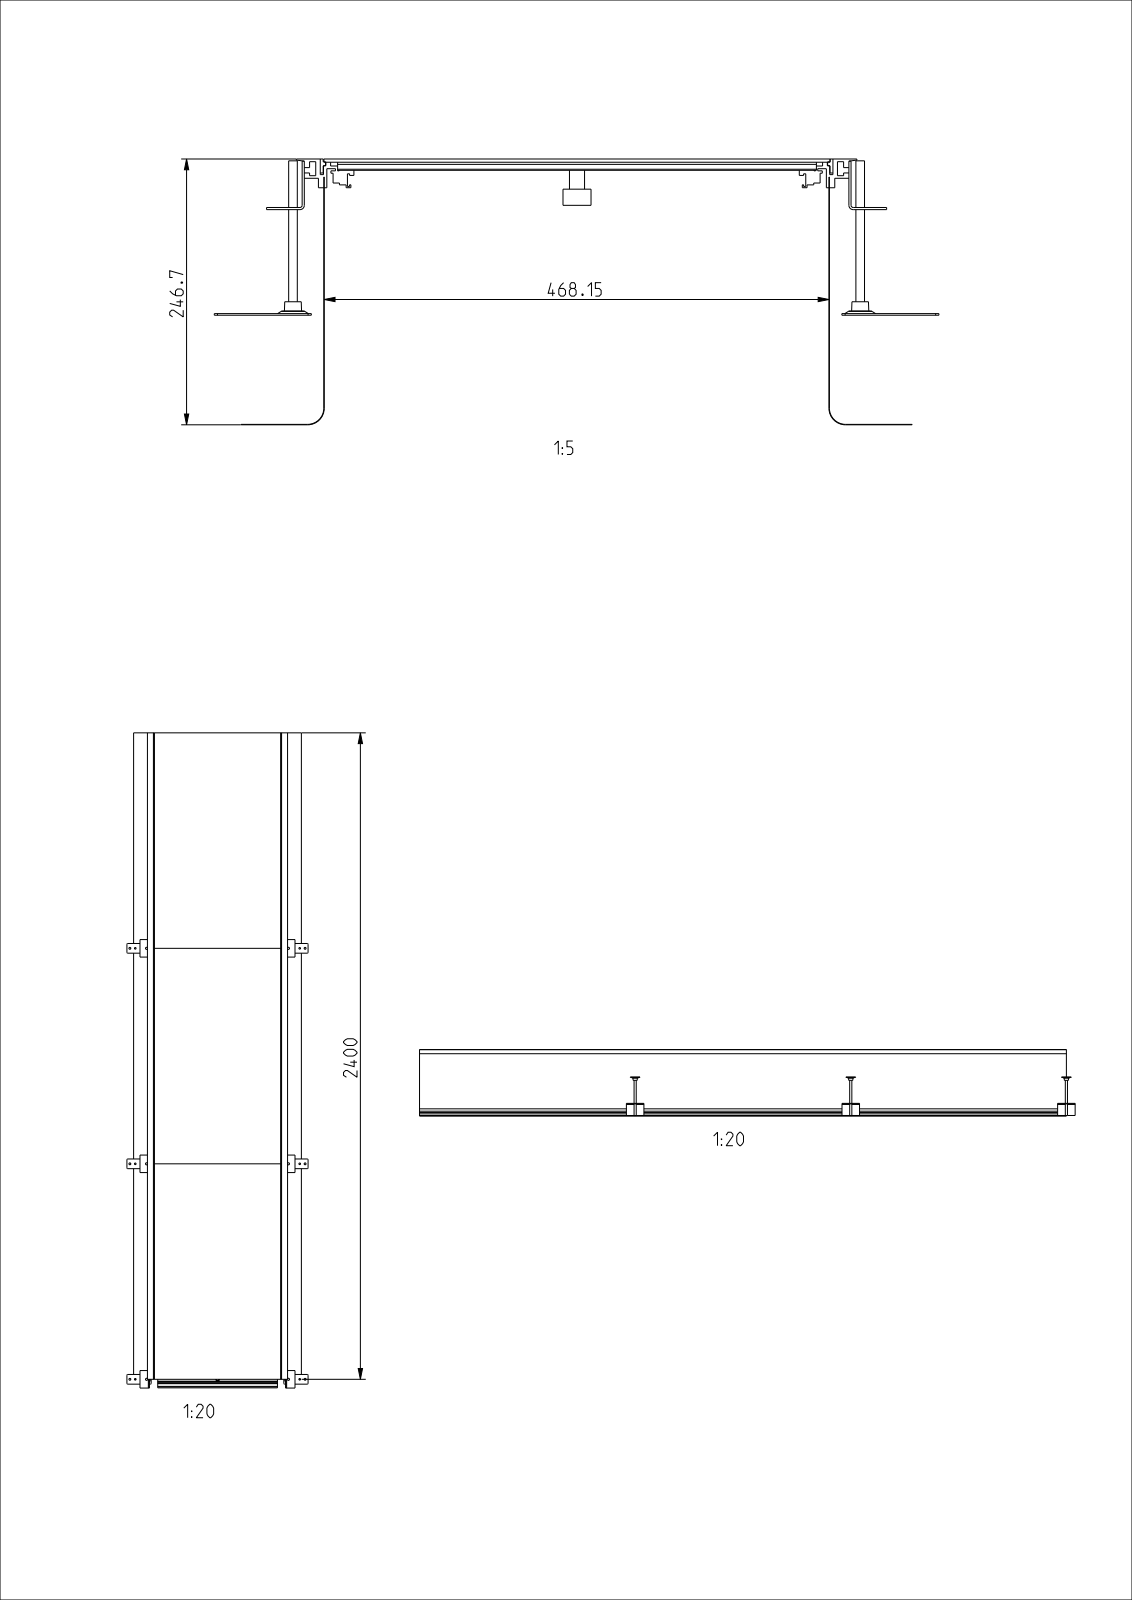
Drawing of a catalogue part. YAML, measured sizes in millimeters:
part_name: "U05644KUN; U05650KUN; U05647KUN; U05826KUN (+8 more)"
step_written_by: "CREO PARAMETRIC BY PTC INC, 2020281 (AUTOMOTIVE_DESIGN)"
units: millimeters
bodies: {solids: 62, faces: 1026, planar: 600, cylindrical: 354, other: 72}
overall_size: [2432.5, 672.13, 246.7]
volume: 8267000
surface_area: 7547000
round_holes:
  - {diameter: 7, count: 15}
  - {diameter: 8, count: 9}
  - {diameter: 10, count: 9}
  - {diameter: 6, count: 6}
  - {diameter: 8.5, count: 6}
  - {diameter: 11.5, count: 6}
  - {diameter: 17.5, count: 6}
  - {diameter: 23, count: 6}
round_bosses_or_shafts:
  - {diameter: 26, count: 9}
  - {diameter: 14, count: 9}
  - {diameter: 11.9, count: 9}
  - {diameter: 20, count: 6}
  - {diameter: 8, count: 6}
partial_cylinders:
  - {radius: 2, count: 92}
  - {radius: 3, count: 24}
  - {radius: 0.5, count: 20}
  - {radius: 4, count: 2}
  - {radius: 15, count: 2}
  - {radius: 15.4, count: 2}
face_to_face_distances: [0.4, 3, 468.55, 468.95, 468.15, 243.7, 246.7, 243.3, 246.3, 6.5]
hole_center_spacings: [800, 1600, 800.25, 801.1, 802.4, 981.21, 992.92, 1018.36]
